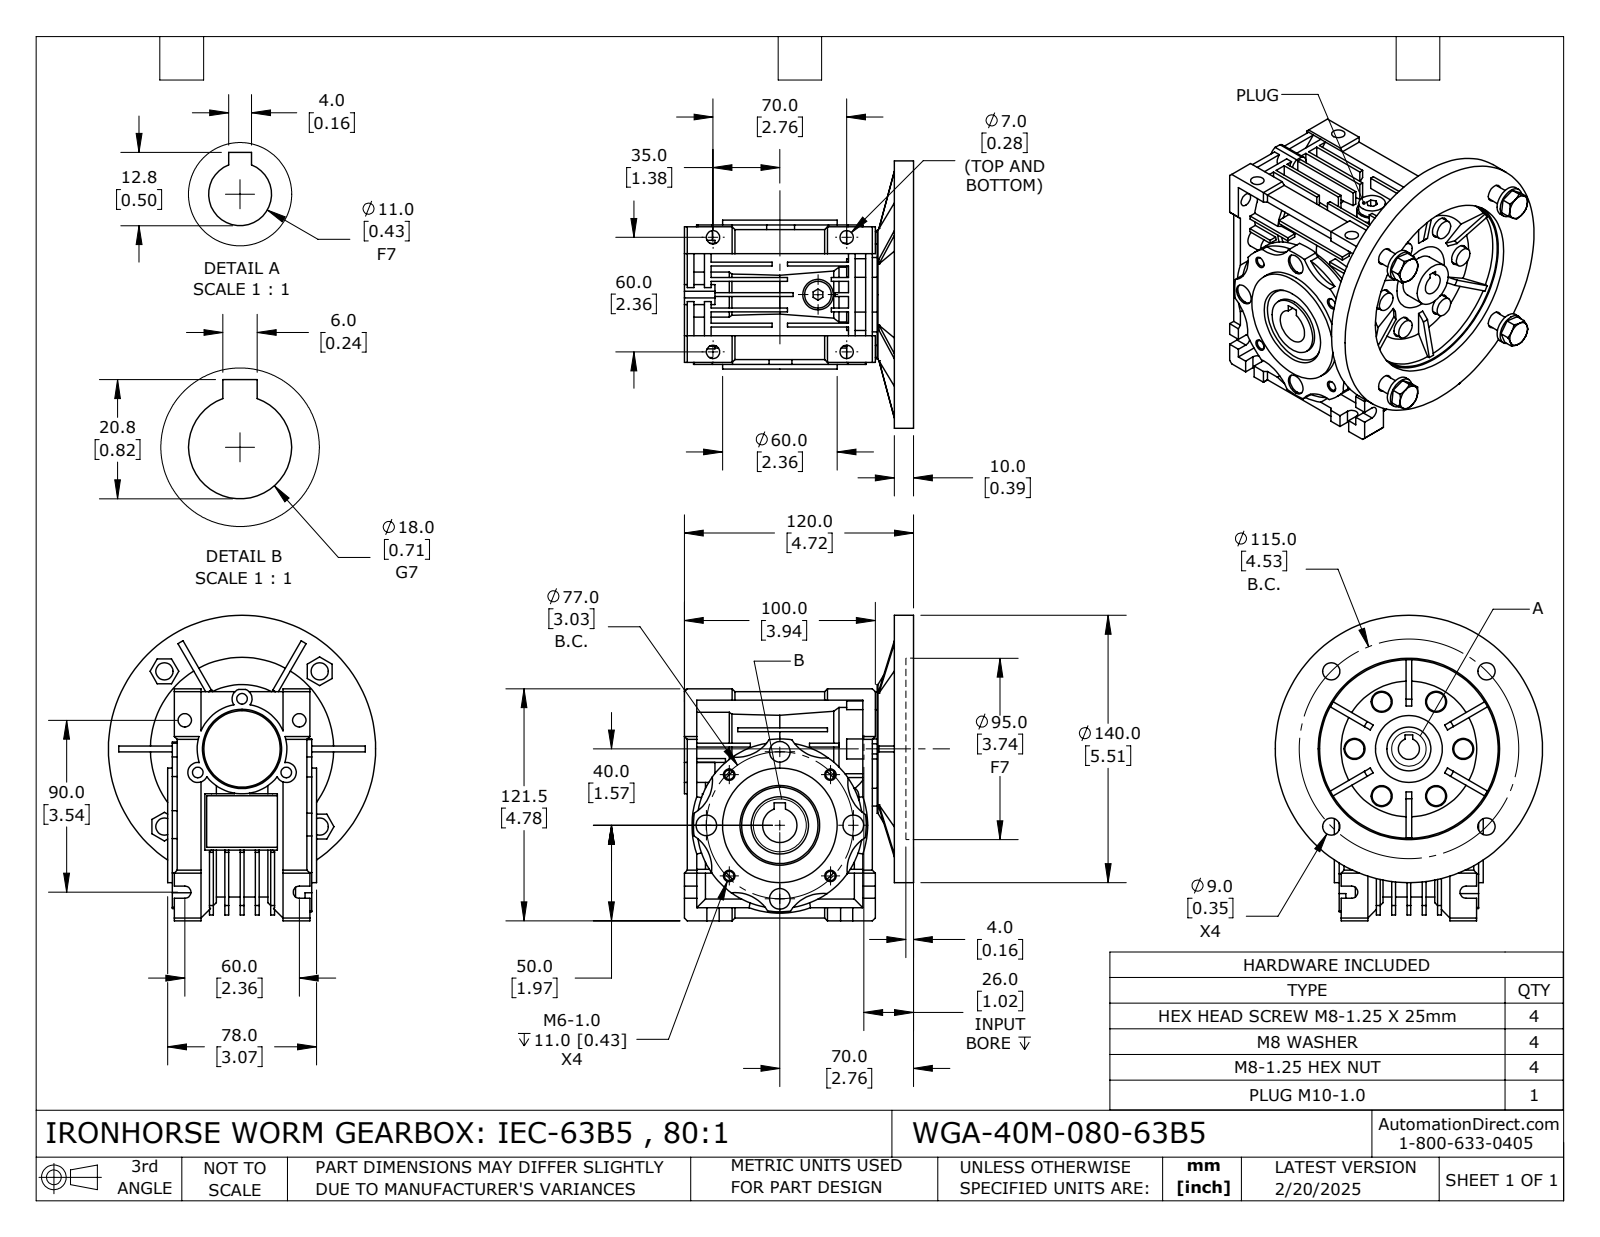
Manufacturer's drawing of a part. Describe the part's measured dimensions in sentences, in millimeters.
The part is named "WGA-40M-080-63B5". Its 3-D file was written by "SolidWorks 2024 (CONFIG_CONTROL_DESIGN)". It is 18 solids with 1083 faces: 592 planar, 298 cylindrical and 193 other. Overall it measures 160 by 140 by 137.98 millimeters. Its volume is 749 957 cubic millimeters and its surface area 190 617 square millimeters. Round holes: 7 of diameter 11, 6 of diameter 7, 5 of diameter 9, 4 of diameter 4.92, 4 of diameter 6.8, 4 of diameter 8, 4 of diameter 9.12, 4 of diameter 10.8, 3 of diameter 5.55, 1 of diameter 11.5, 1 of diameter 18, 1 of diameter 23. Round bosses or shafts: 6 of diameter 10, 5 of diameter 16, 1 of diameter 140, 1 of diameter 75, 1 of diameter 67.5, 1 of diameter 60, 1 of diameter 54, 1 of diameter 47. Partial cylindrical surfaces (rounded edges, fillets, slot ends): 8 of radius 20, 6 of radius 3.2, 6 of radius 5.22, 3 of radius 5.25, 1 of radius 43.5, 1 of radius 43.59, 1 of radius 45.25, 1 of radius 46. The main face-to-face distances are 10, 8, 6, 2, 5, 1.5, 16, 24, 14, 2.5. The hole center spacings are 28.5, 29.1, 70.22, 49.36, 30.87, 33.54, 37.5, 38.5.
